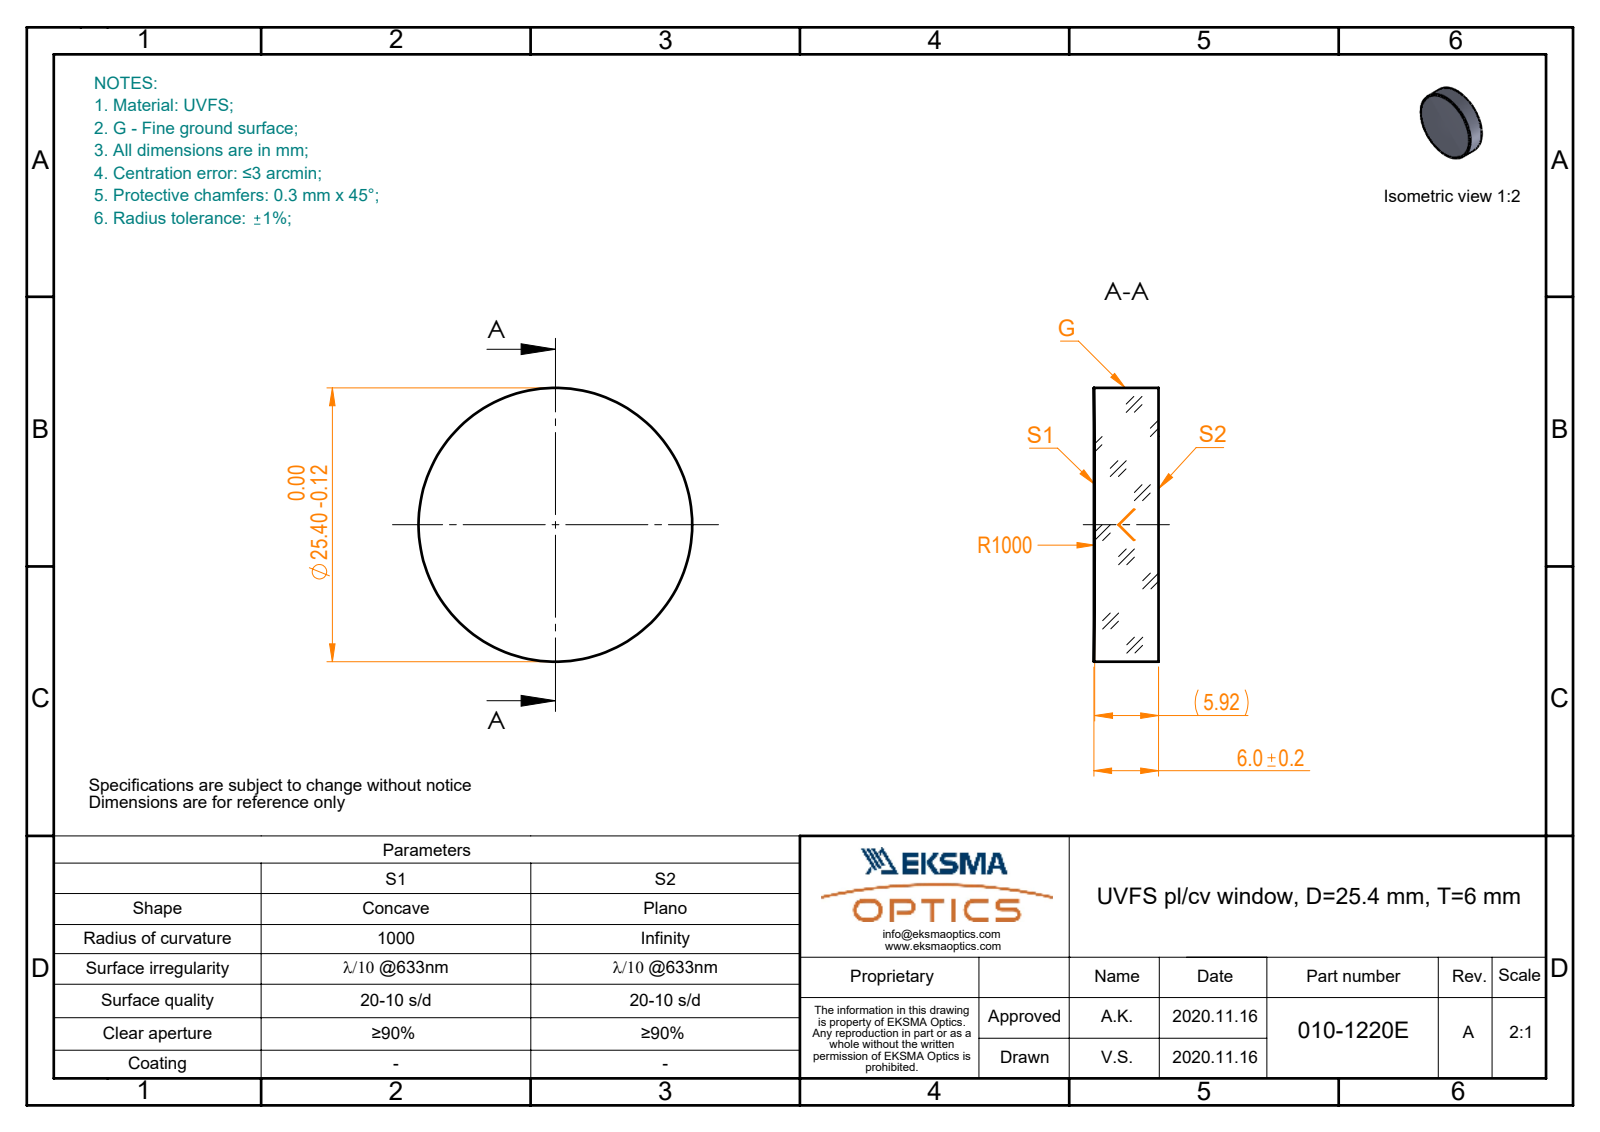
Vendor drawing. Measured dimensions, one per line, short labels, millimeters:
name: 010-1220E_UVFS_PCV_window
written by: SolidWorks 2019 (CONFIG_CONTROL_DESIGN)
unit: mm
bodies: 1 solid, 5 faces (1 planar, 2 cylindrical, 2 other)
size: 25.4 × 25.4 × 6
volume: 3 020 mm³; area: 1 492 mm²
bosses: 1× ⌀25.4
